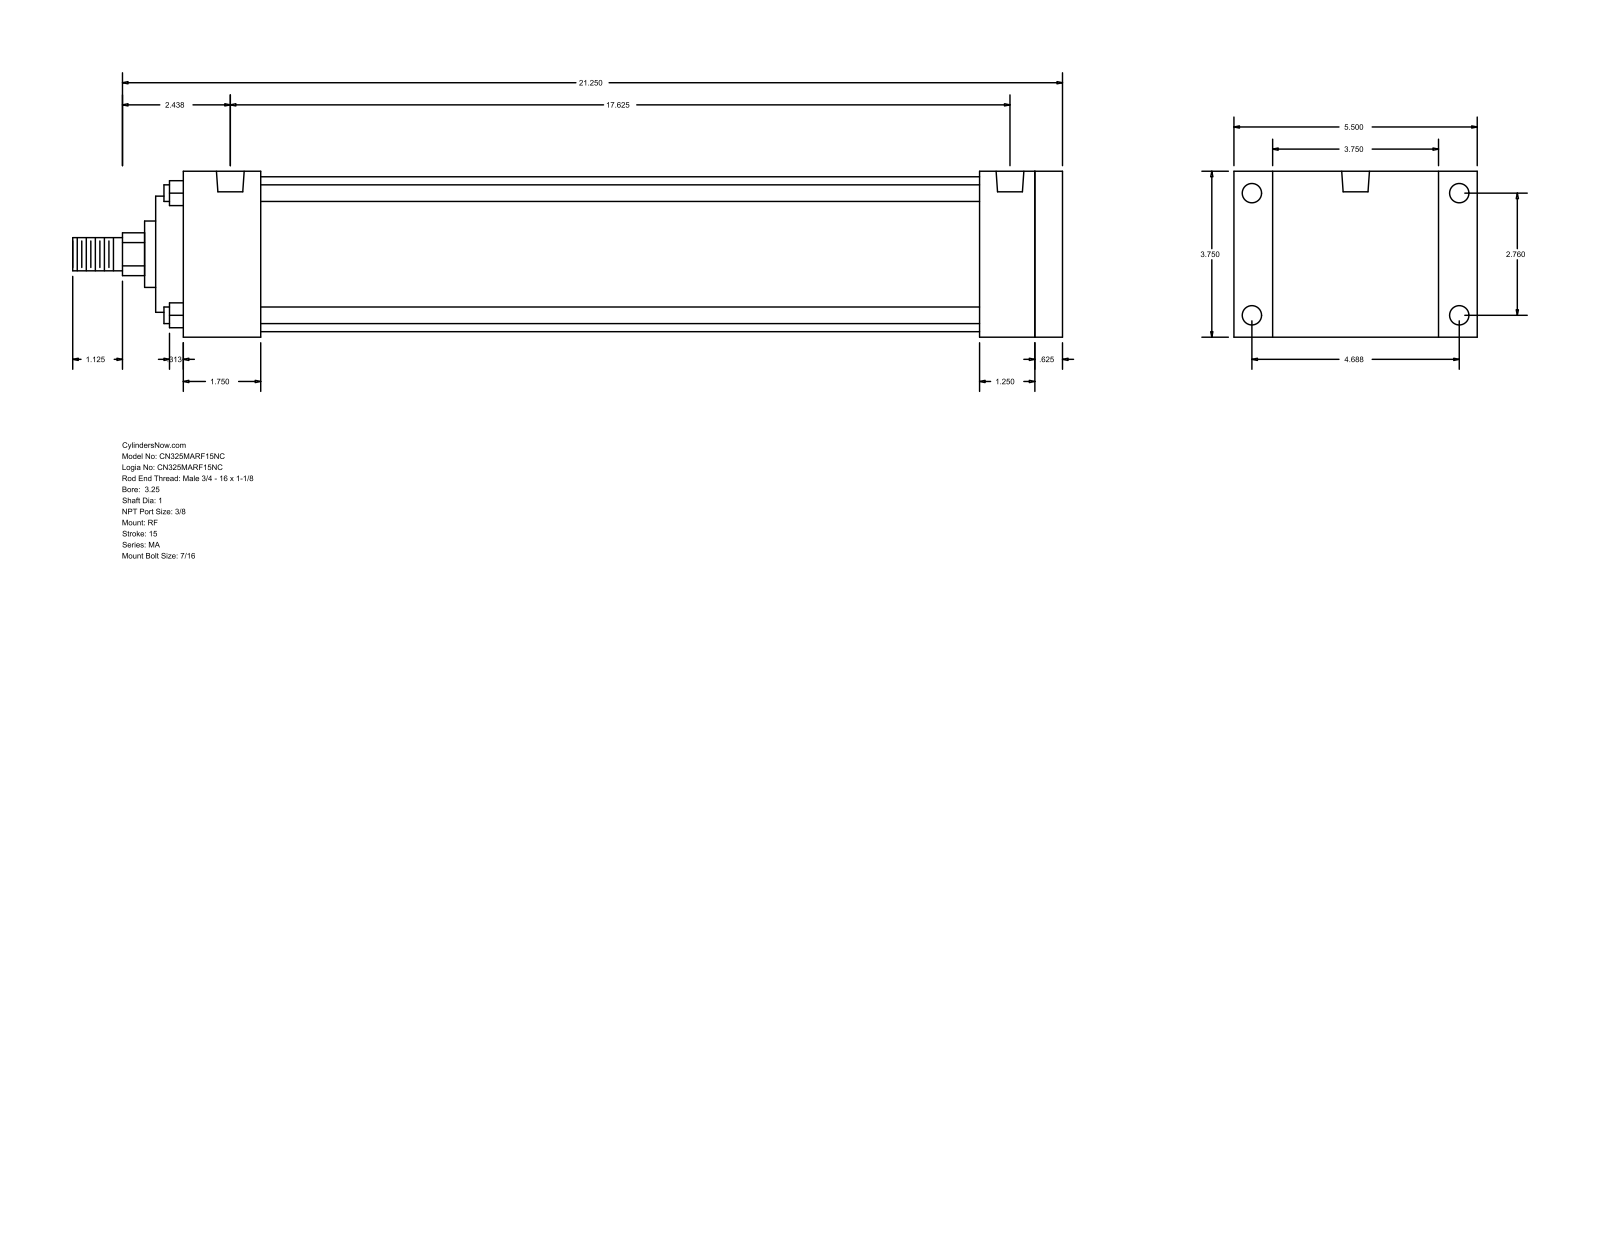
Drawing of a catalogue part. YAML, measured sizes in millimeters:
part_name: "MA_RF__0325_1"
step_written_by: "GSSL Pune (CONFIG_CONTROL_DESIGN)"
units: millimeters
bodies: {solids: 0, faces: 94, planar: 65, cylindrical: 29, other: 0}
overall_size: [568.33, 139.7, 95.25]
round_holes:
  - {diameter: 11.11, count: 8}
  - {diameter: 15.93, count: 2}
round_bosses_or_shafts:
  - {diameter: 9.53, count: 4}
  - {diameter: 88.9, count: 1}
  - {diameter: 66.67, count: 1}
  - {diameter: 38.1, count: 1}
  - {diameter: 25.4, count: 1}
  - {diameter: 19.05, count: 1}
partial_cylinders:
  - {radius: 12.29, count: 1}
face_to_face_distances: [95.24, 504.83, 15.87, 488.96, 22.23, 117.47, 457.2, 31.76, 47.63, 44.46]
hole_center_spacings: [70.1, 119.06, 138.16, 438.15, 4.76, 4.77, 442.91, 442.92]
